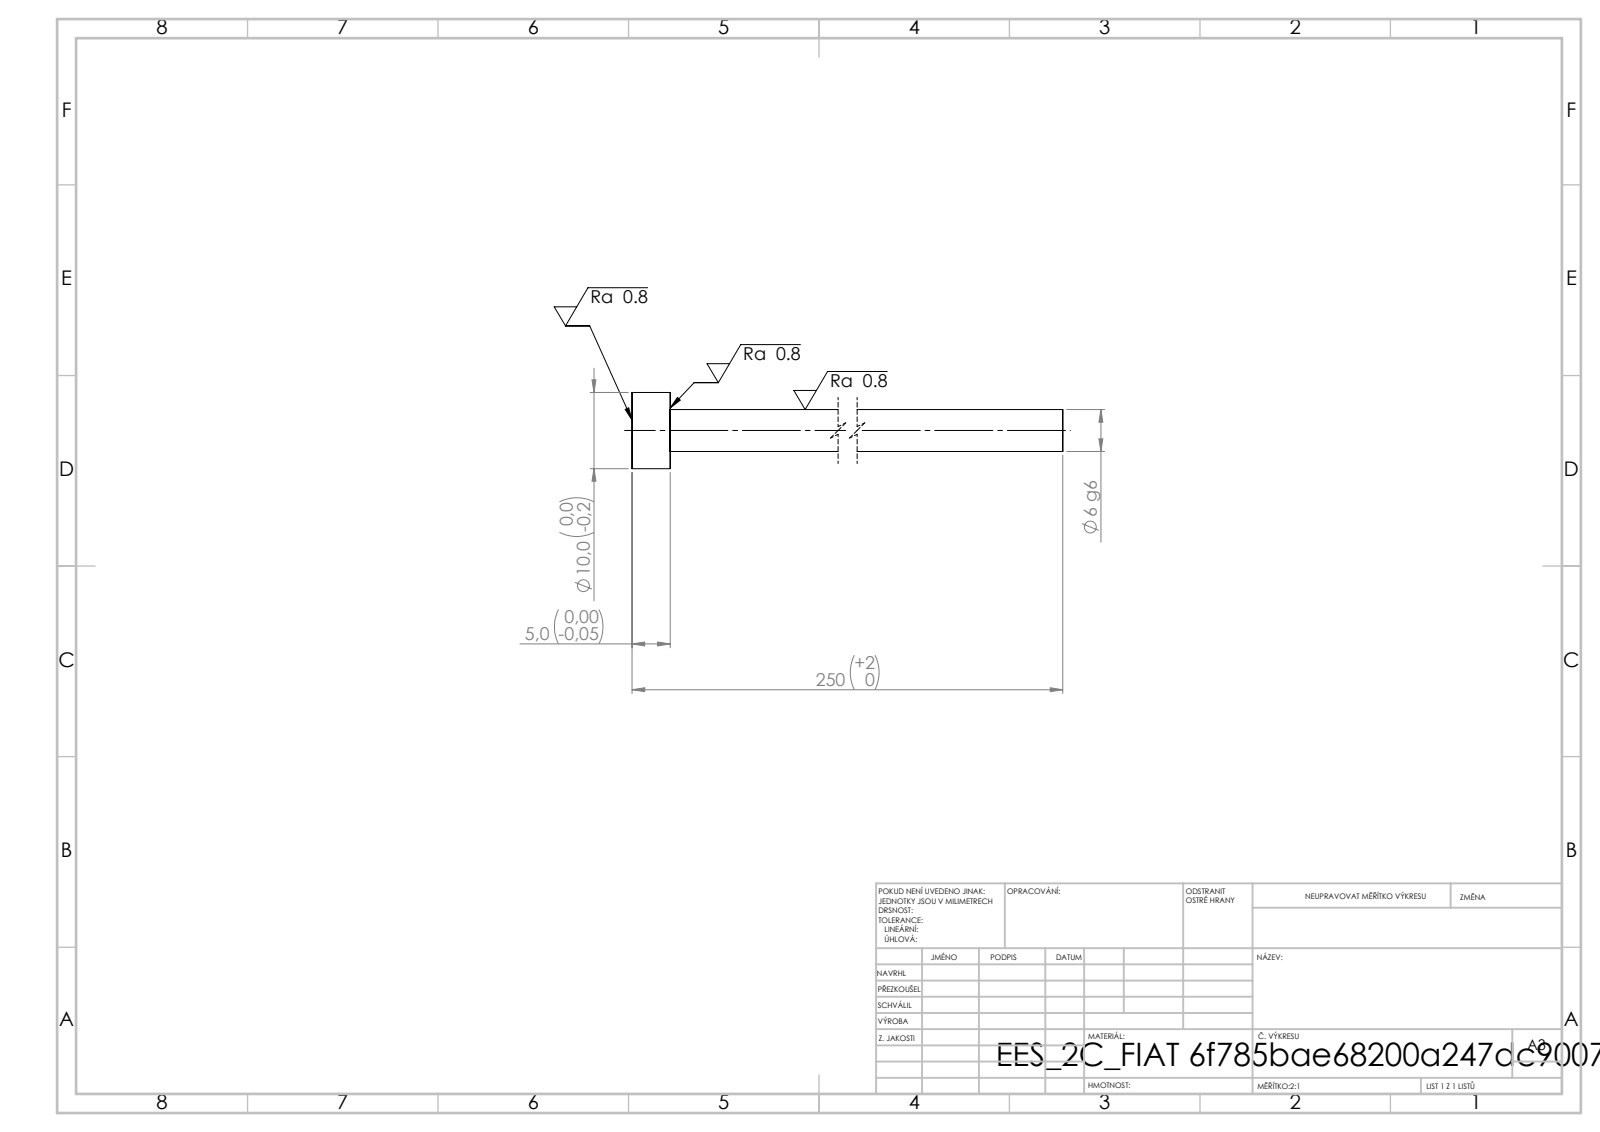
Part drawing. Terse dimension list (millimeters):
written by: SolidWorks 2019 (CONFIG_CONTROL_DESIGN)
unit: mm
bodies: 1 solid, 7 faces (3 planar, 4 cylindrical, 0 other)
size: 250 × 10 × 10
volume: 6 213 mm³; area: 4 547 mm²
bosses: 1× ⌀10, 1× ⌀5.5
face distances: 5, 250, 245
